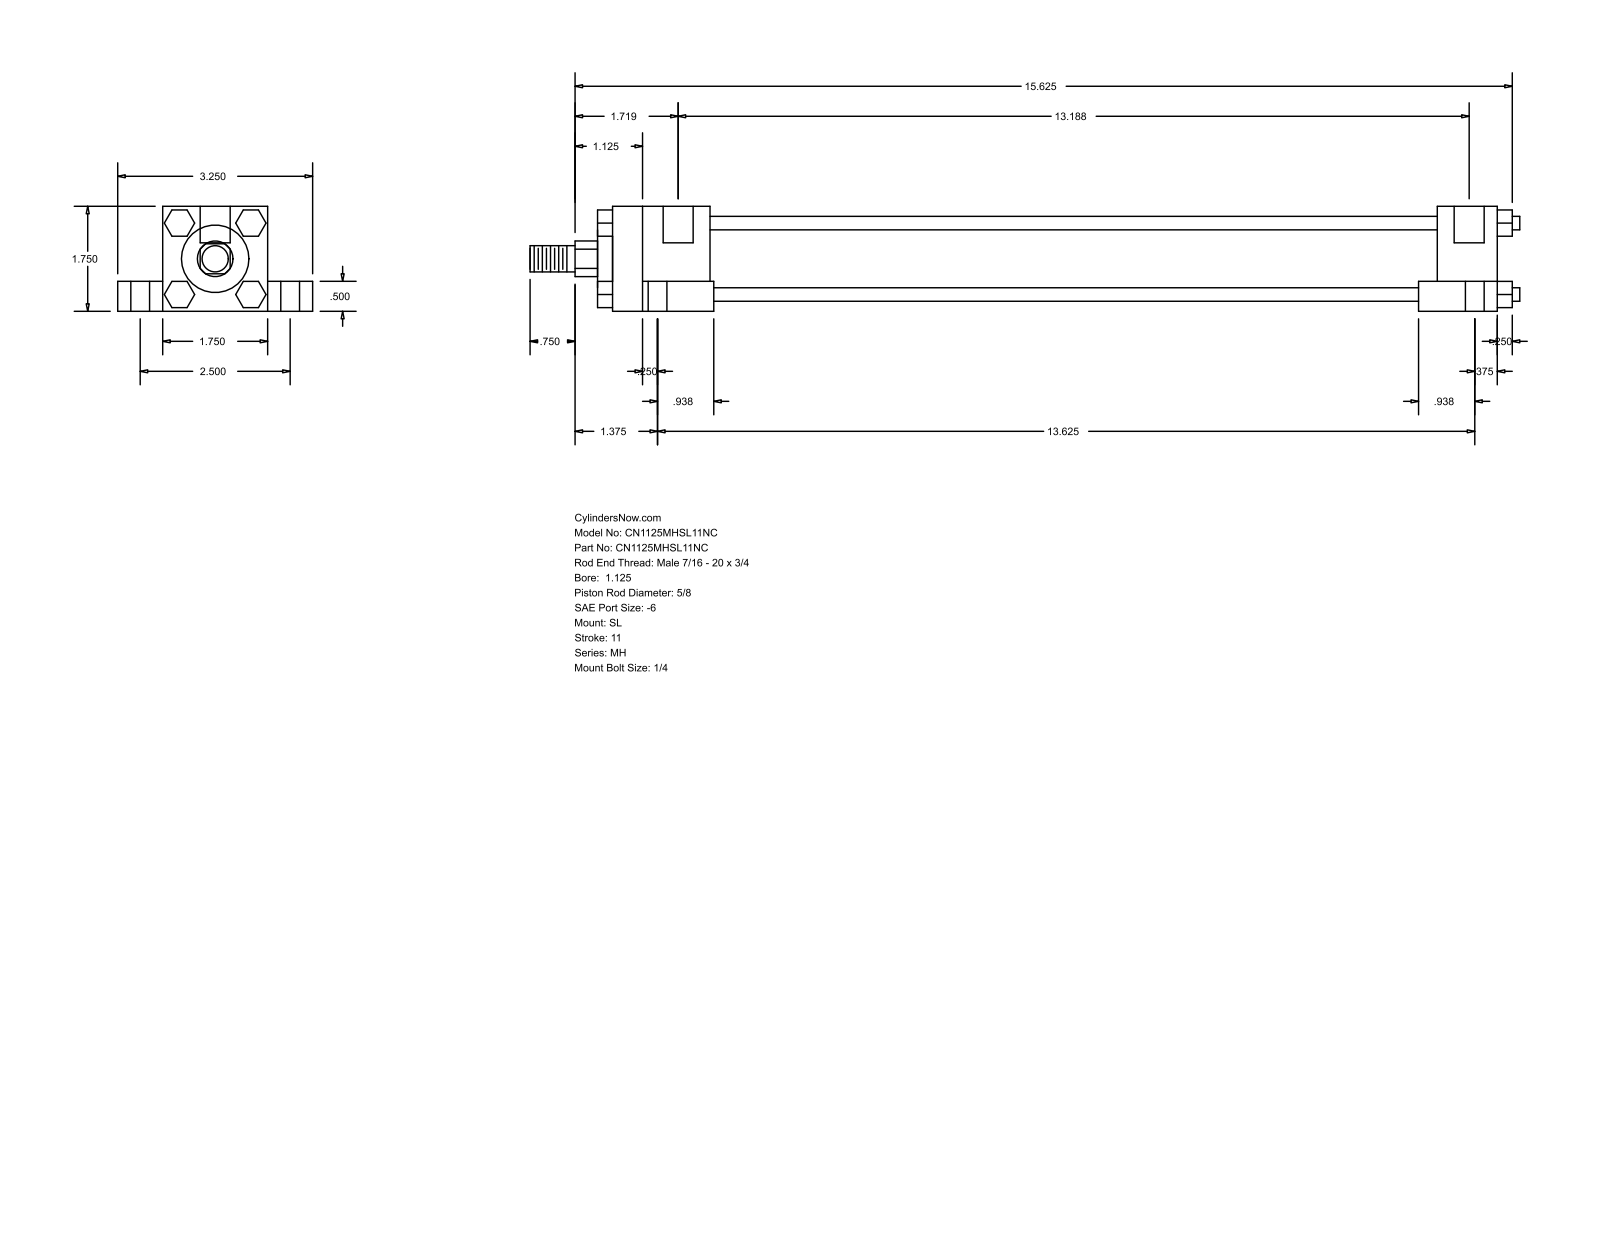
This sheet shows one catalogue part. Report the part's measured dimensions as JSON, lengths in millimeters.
{"part_name": "MH_SL__0112_0.625", "step_written_by": "GSSL Pune (CONFIG_CONTROL_DESIGN)", "units": "millimeters", "bodies": {"solids": 0, "faces": 150, "planar": 114, "cylindrical": 36, "other": 0}, "overall_size": [419.1, 82.55, 44.45], "round_holes": [[5.56, 4], [7.94, 4], [14.29, 4], [12.7, 2]], "round_bosses_or_shafts": [[5.71, 4], [34.92, 1], [28.57, 1], [15.88, 1], [11.11, 1]], "partial_cylinders_radius": [[7.54, 1]], "face_to_face_distances": [44.46, 31.76, 19.04, 12.7, 63.5, 11.11, 47.62, 25.4, 307.97, 333.37], "hole_center_spacings": [31.84, 32.23, 32.93, 63.5, 331.79, 335.67, 338.83, 342]}
